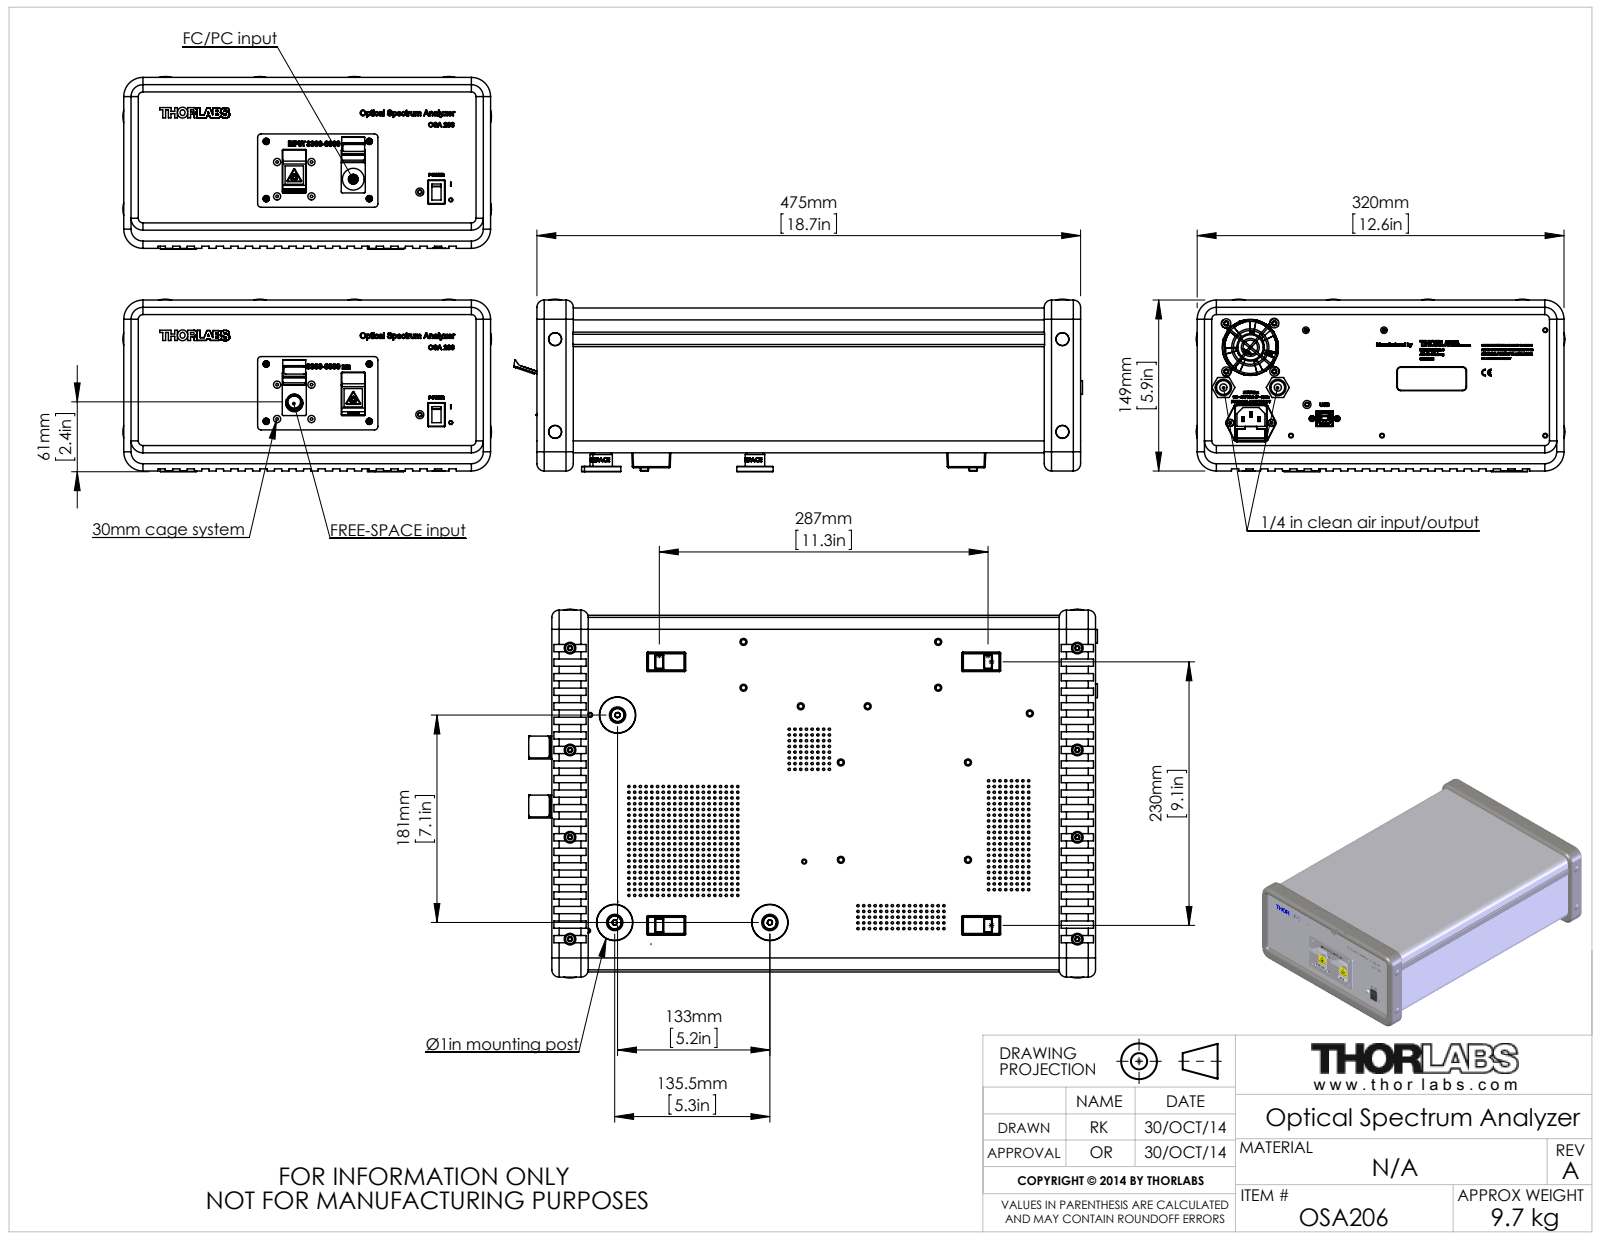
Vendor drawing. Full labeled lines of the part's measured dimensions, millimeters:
Part name (STEP PRODUCT): STN012216-E0W
STEP written by: SolidWorks 2014 (AUTOMOTIVE_DESIGN)
Units: millimetres
Bodies: 0 solids, 1938 faces (771 planar, 998 cylindrical, 169 other)
Overall size (bounding box): 496.54 × 321.82 × 150.61
Round holes (diameter × count): ⌀2 ×654, ⌀11.43 ×12, ⌀10.16 ×8, ⌀6.3 ×4, ⌀6.35 ×2, ⌀2.26 ×1, ⌀49 ×1
Round bosses / shafts (diameter × count): ⌀11.05 ×10, ⌀12 ×5, ⌀8 ×4, ⌀31.75 ×3, ⌀18.4 ×3, ⌀17 ×3, ⌀1.5 ×3, ⌀14.3 ×2
Partial cylindrical surfaces — rounded edges, fillets, slot ends (radius × count): R0.91 ×35, R0.5 ×32, R1 ×31, R6.35 ×18, R0.27 ×15, R0.38 ×10, R1.6 ×6, R1.9 ×4
Main face-to-face distances: 1, 125.4, 126.4, 124.4, 306.6, 305.6, 307.6, 3.8, 4.8, 120.6
Hole centre spacings: 11.18, 5, 15.81, 7.07, 10, 18.03, 20.62, 14.14
